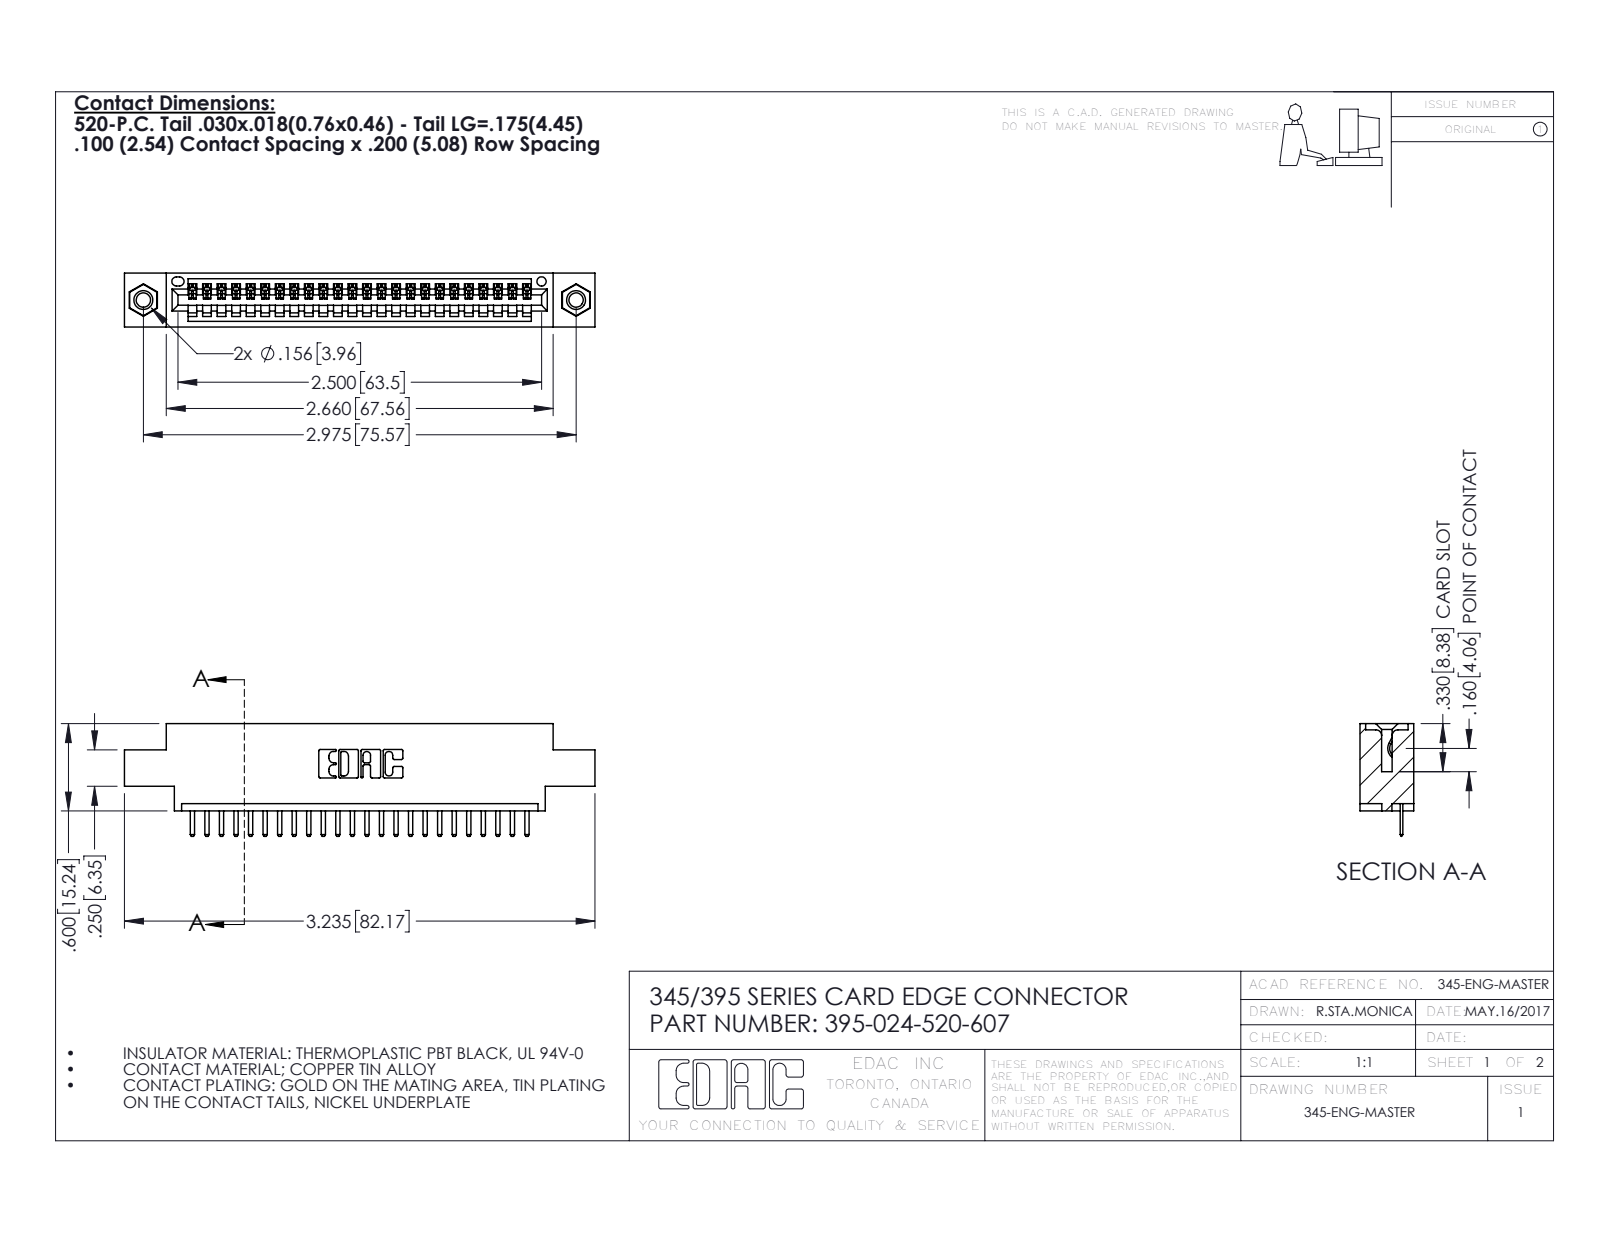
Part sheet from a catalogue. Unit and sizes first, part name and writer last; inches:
Units: inches
Overall size (bounding box): 3.235 × 0.775 × 0.37
Round holes (diameter × count): ⌀0.098 ×2, ⌀0.125 ×2, ⌀0.156 ×2, ⌀0.064 ×1
Round bosses / shafts (diameter × count): ⌀0.155 ×2
Partial cylindrical surfaces — rounded edges, fillets, slot ends (radius × count): R0.01 ×50, R0.006 ×48, R0.01 ×22, R0.007 ×6, R0.031 ×6, R0.026 ×3, R0.031 ×2, R0.04 ×2
Main face-to-face distances: 0.072, 0.298, 0.37, 0.2, 0.098, 0.272, 0.025, 0.225, 0.072, 0.175
Hole centre spacings: 0.27, 2.741, 2.975
Volume: 0.455 in³ · Surface area: 14.89 in²
Bodies: 27 solids, 1678 faces (1124 planar, 538 cylindrical, 16 other)
Part name (STEP PRODUCT): 345-250-001_345-250-005-103; 345 Part_0.170 Offset - 0.156 Dia-TI; 395-024-520-607; 345-292-001_345-293-120
STEP written by: SolidWorks 2016 (CONFIG_CONTROL_DESIGN)
